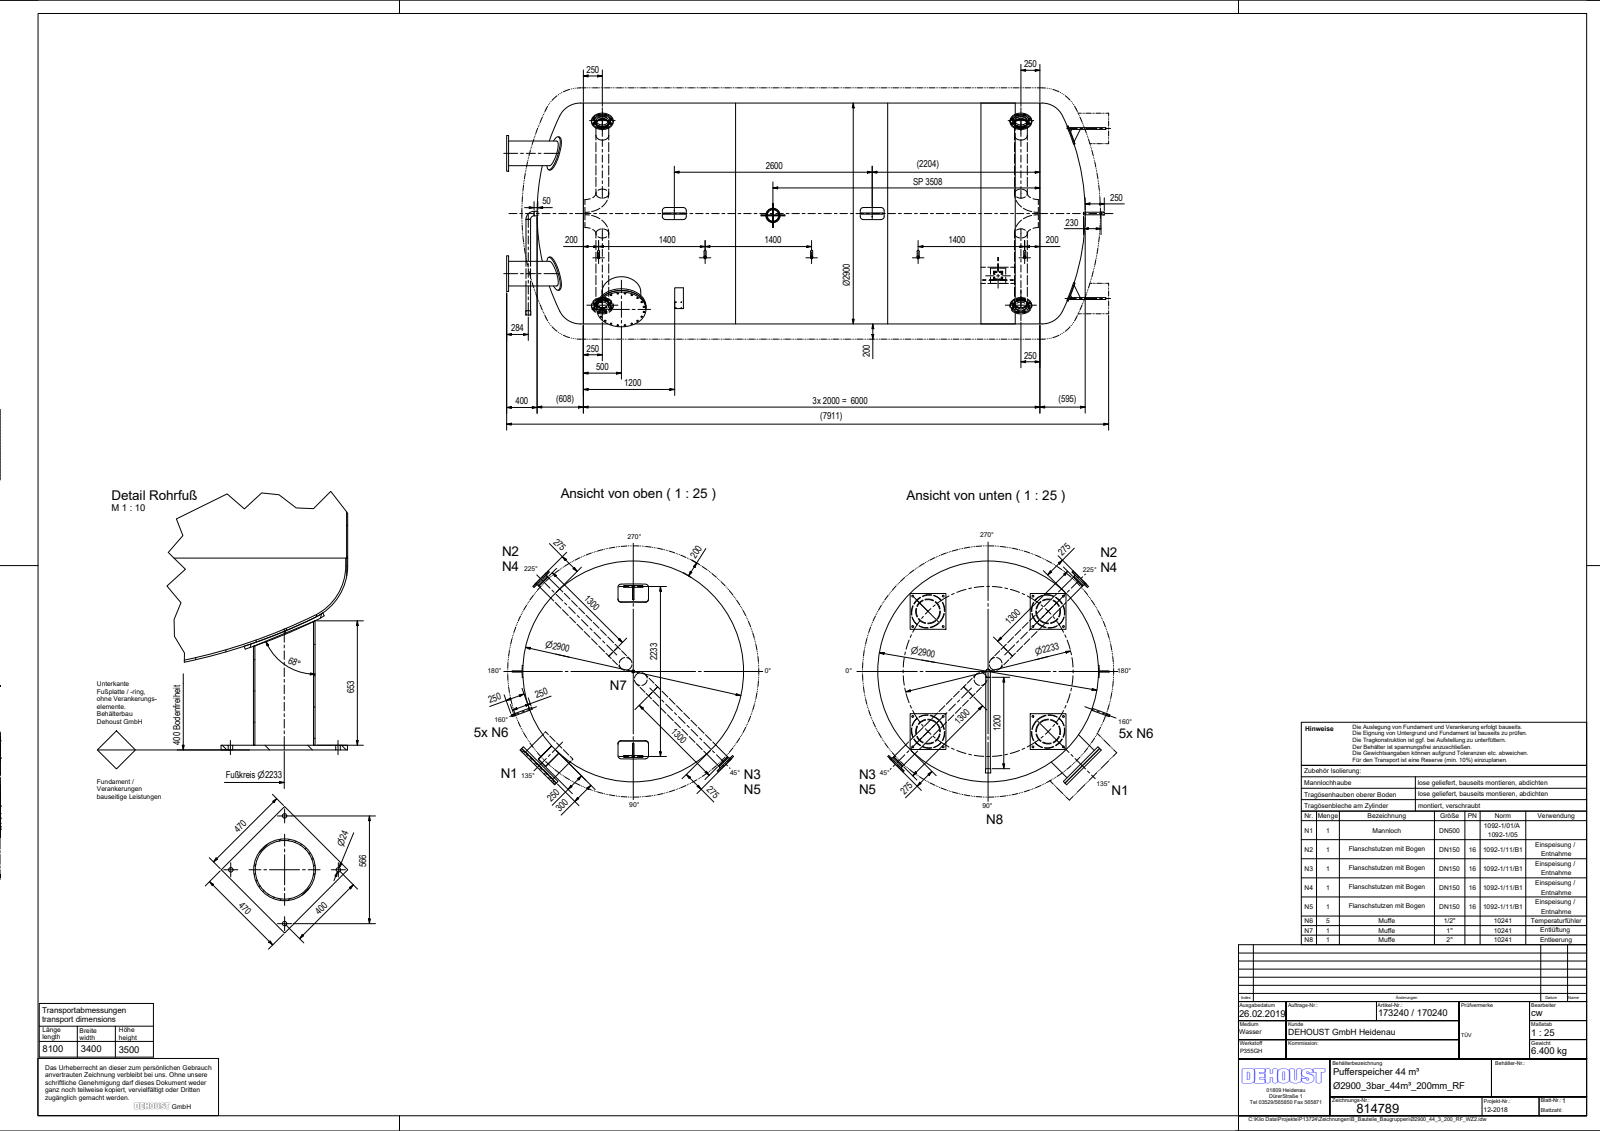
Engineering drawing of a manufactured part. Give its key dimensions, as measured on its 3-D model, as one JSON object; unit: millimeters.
{"part_name": "Ø2900_44_3_200_RF_WZ2; Klöpper_Gew_Ø2900_7,5; Klöpper_Gew_Ø2900_10,3; Zyl_Ø2900_6x6000_2019 (+8 more)", "step_written_by": "Autodesk Inventor 2019 (AUTOMOTIVE_DESIGN)", "units": "millimeters", "bodies": {"solids": 58, "faces": 449, "planar": 178, "cylindrical": 225, "other": 46}, "overall_size": [7874.41, 3051.99, 2937.4], "volume_mm3": 736600000, "surface_area_mm2": 165100000, "round_holes": [[22, 64], [24, 16], [159.3, 8], [18.63, 5], [21.7, 5], [26.9, 5], [5.8, 4], [168.3, 4], [307.9, 4], [5, 2], [52.3, 2], [508, 2]], "round_bosses_or_shafts": [[168.3, 8], [26.9, 5], [26.4, 5], [450, 4], [323.9, 4], [285, 4], [212, 4], [2900, 1]], "partial_cylinders_radius": [[42, 16], [10, 6], [6, 4], [5, 2], [36, 2], [72, 2], [125, 1], [1460, 1]], "face_to_face_distances": [25, 600, 3785.46, 4230.46, 3760.46, 4205.46, 445, 27.99, 2777.5, 3222.5], "hole_center_spacings": [120, 300, 185.41, 93.86, 1400, 5500, 352.67, 169.71]}
